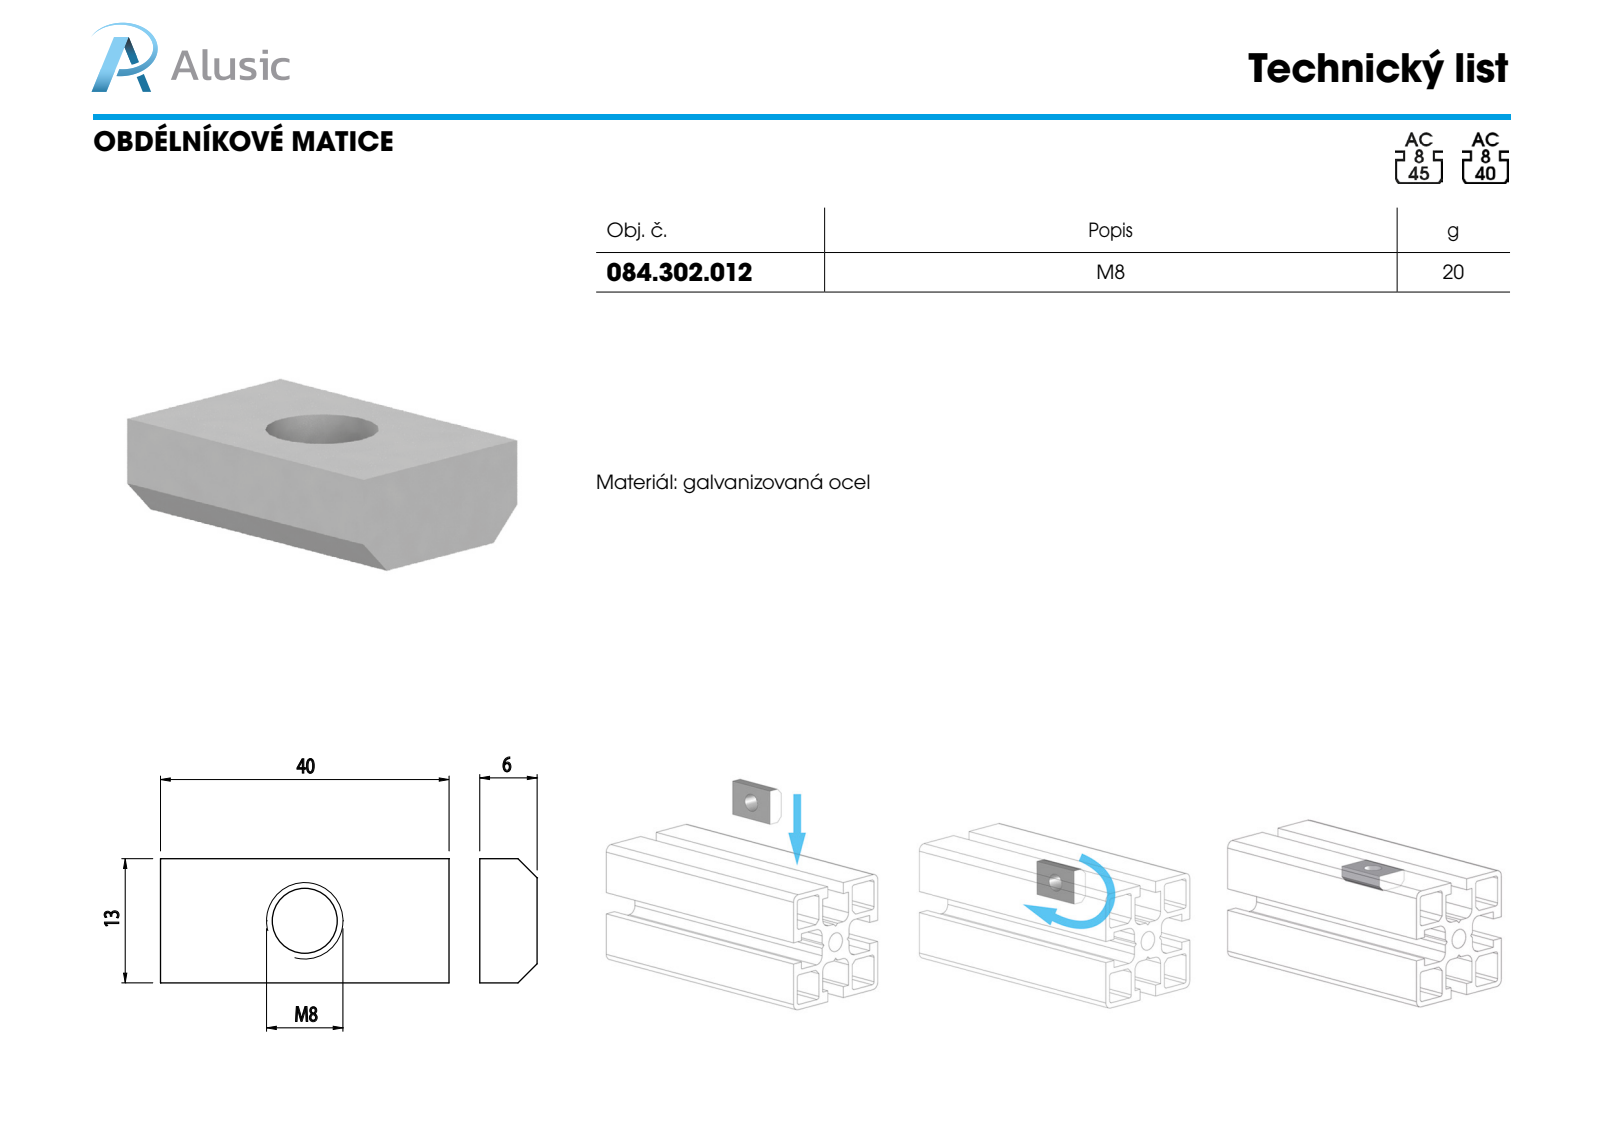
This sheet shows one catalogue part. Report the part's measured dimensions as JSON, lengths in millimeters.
{"part_name": "084.302.012", "step_written_by": "SolidWorks 2011 (CONFIG_CONTROL_DESIGN)", "units": "millimeters", "bodies": {"solids": 1, "faces": 10, "planar": 8, "cylindrical": 2, "other": 0}, "overall_size": [40, 13, 6], "volume_mm3": 2742, "surface_area_mm2": 1630, "round_holes": [[6.8, 1]], "face_to_face_distances": [6, 13, 40]}
